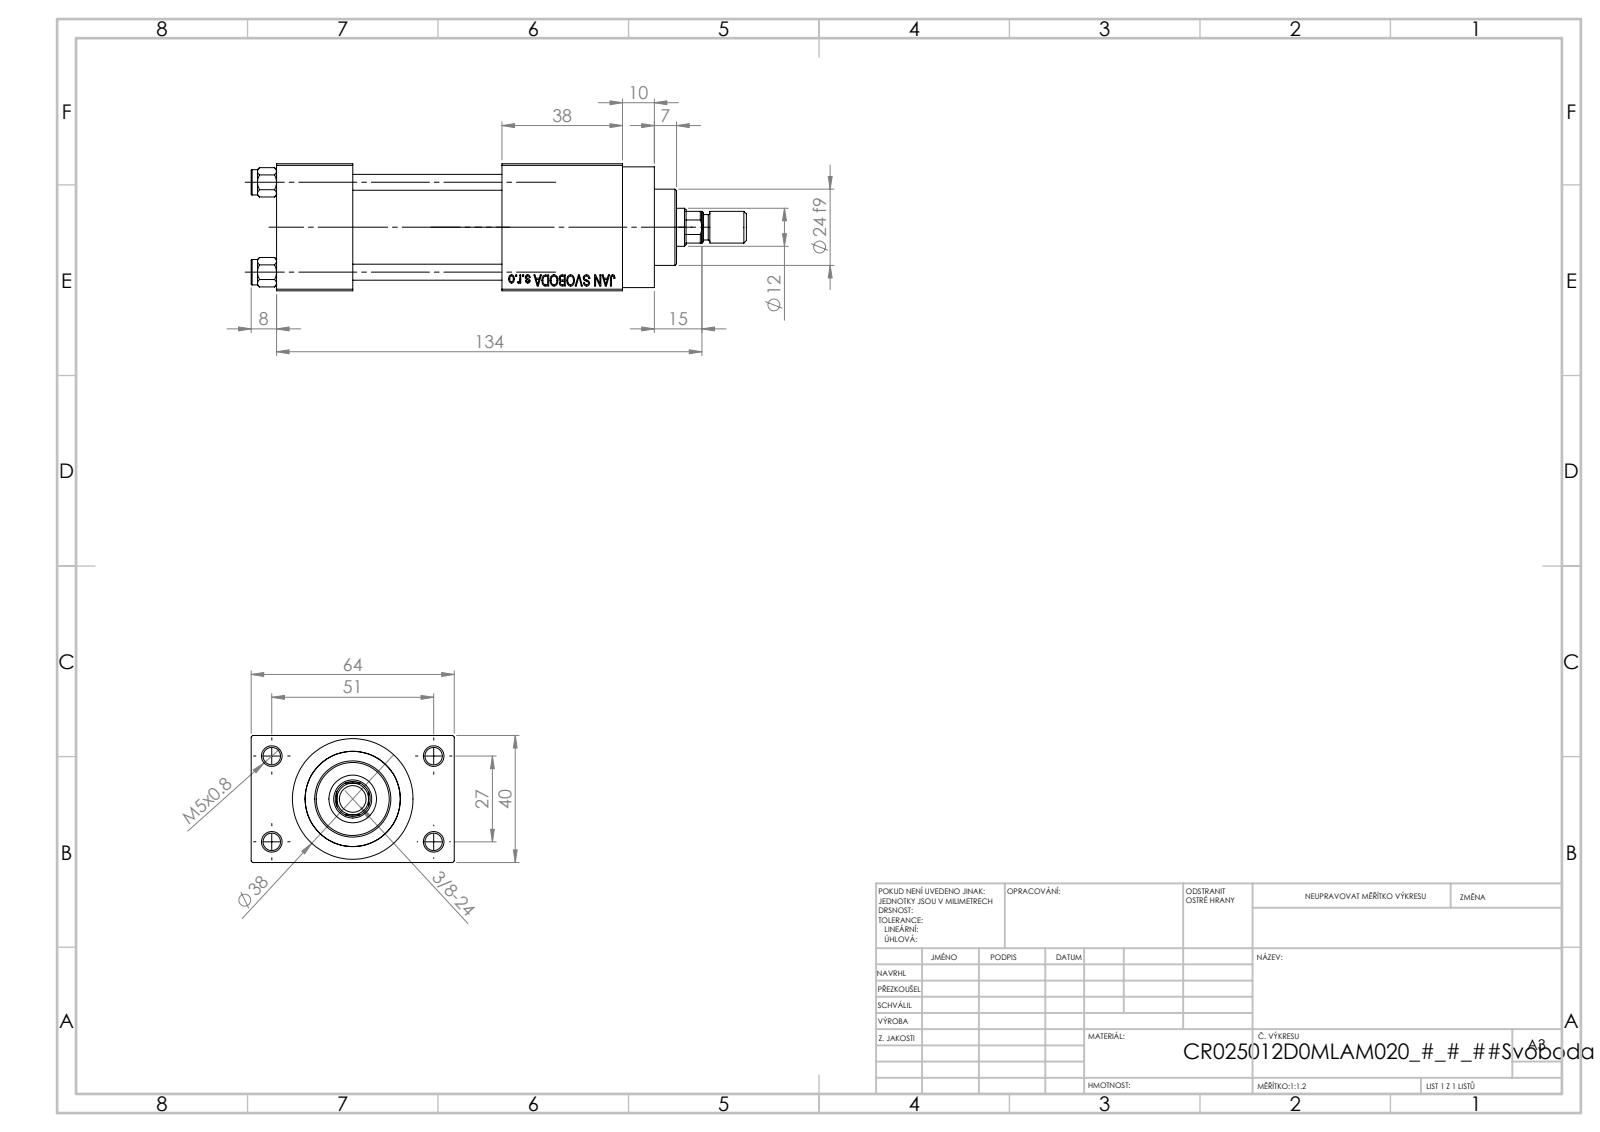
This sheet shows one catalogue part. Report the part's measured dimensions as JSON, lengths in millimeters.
{"part_name": "V215CR_D_TYCINKA; V215CR_VCP_D; V215CR_D_Body; V215_VC_A (+2 more)", "step_written_by": "SolidWorks 2019 (CONFIG_CONTROL_DESIGN)", "units": "millimeters", "bodies": {"solids": 12, "faces": 1117, "planar": 500, "cylindrical": 93, "other": 524}, "overall_size": [156, 64, 40], "volume_mm3": 176276, "surface_area_mm2": 62273, "round_holes": [[5, 4], [5.5, 4], [20, 3], [7, 2], [13.16, 2], [6.5, 1], [12, 1], [15, 1], [25, 1], [30, 1]], "round_bosses_or_shafts": [[8, 5], [38, 1], [31, 1], [24, 1], [10, 1]], "partial_cylinders_radius": [[5.5, 1]], "face_to_face_distances": [40, 12, 52, 47, 24, 71, 64, 38, 109, 85], "hole_center_spacings": [11.37, 20.01, 28.3, 28.85, 29.89, 39.66, 48.34, 27]}
